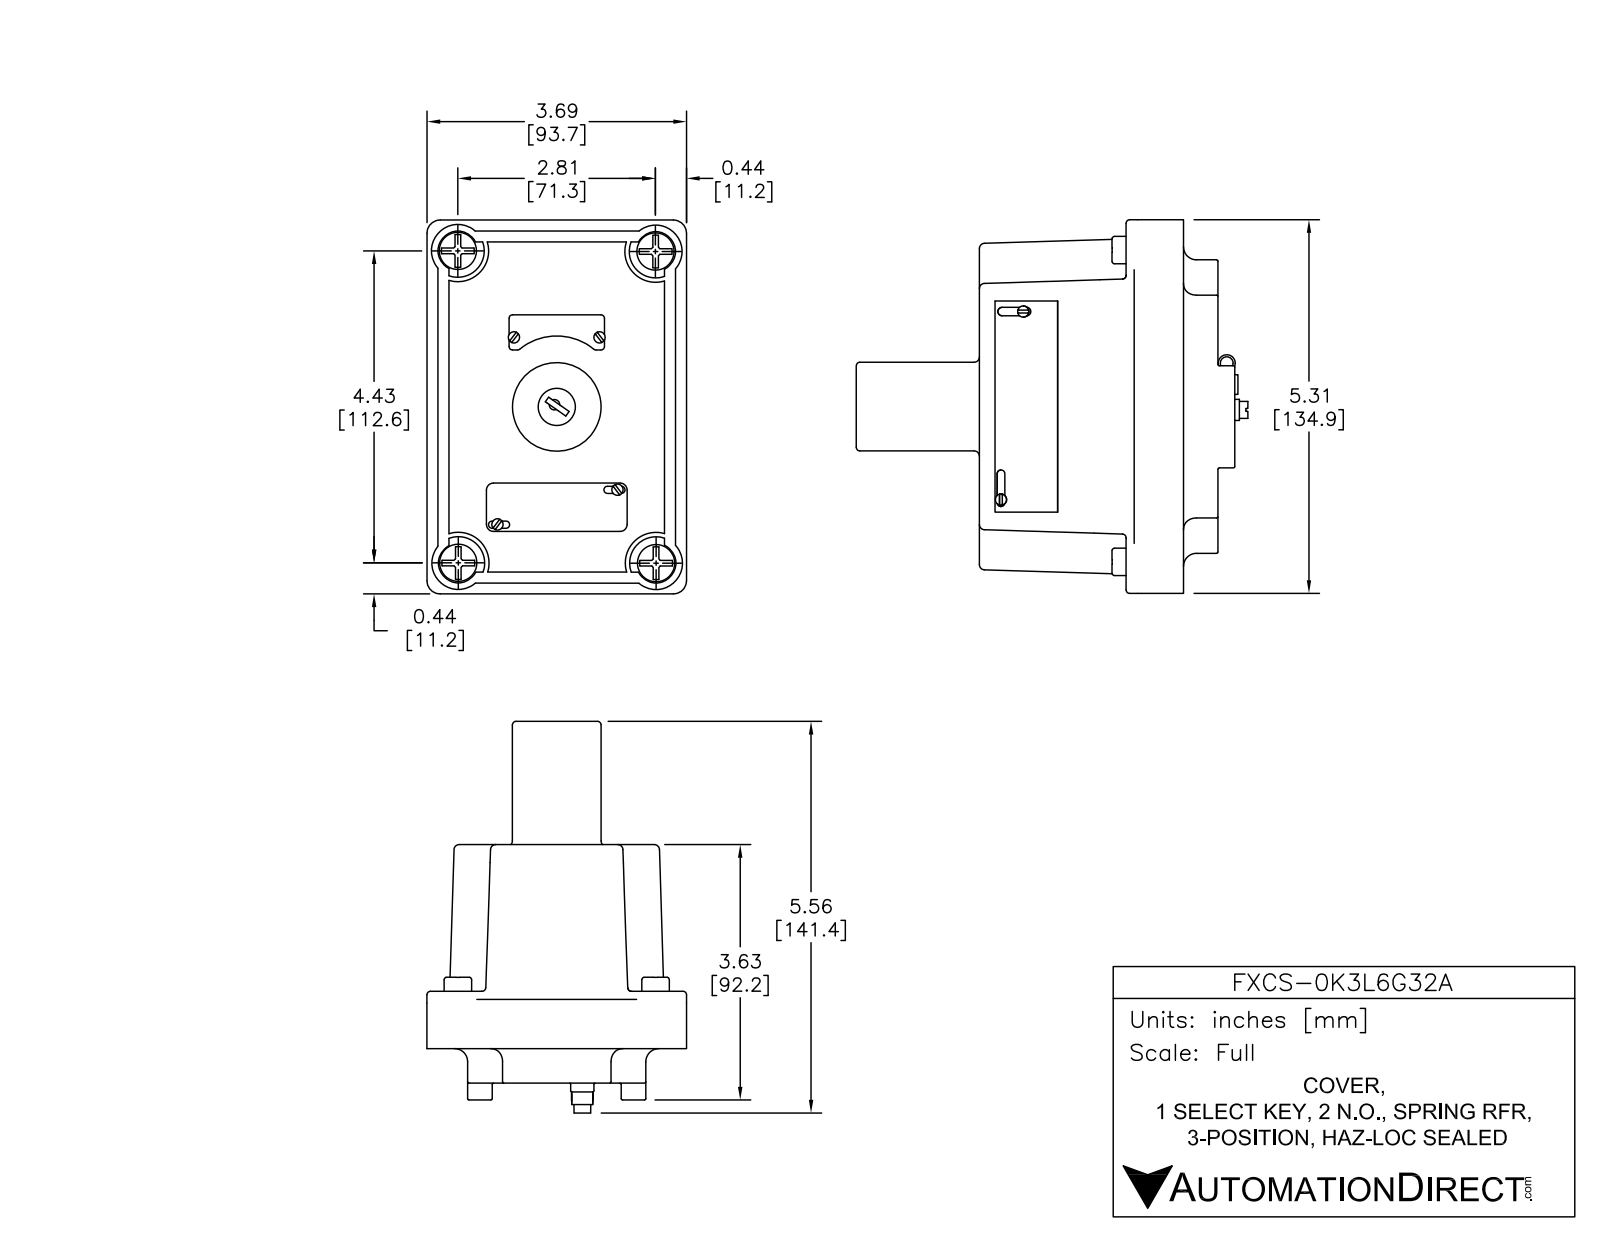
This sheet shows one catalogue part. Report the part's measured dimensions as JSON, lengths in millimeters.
{"part_name": "FXCS-0K3L6G32A", "step_written_by": "SolidWorks 2015 (AUTOMOTIVE_DESIGN)", "units": "millimeters", "bodies": {"solids": 2, "faces": 699, "planar": 303, "cylindrical": 157, "other": 239}, "overall_size": [141.4, 134.9, 93.7], "volume_mm3": 820500, "surface_area_mm2": 63940, "round_holes": [[4.1, 8], [5, 1], [13.4, 1]], "round_bosses_or_shafts": [[4.1, 8], [9.9, 4], [32, 1], [8.4, 1], [7.6, 1], [6.1, 1]], "partial_cylinders_radius": [[1.3, 24], [0.5, 22], [1.3, 4], [1.4, 4], [1.5, 4], [1.9, 4], [2.5, 4], [4.7, 4]], "face_to_face_distances": [86.1, 12.4, 73.7, 0.5, 93.7, 14.7, 79, 30.2, 17.8, 55.9], "hole_center_spacings": [6.4, 55.8, 12.7, 55.4, 56.9, 19.1, 27.7, 28.3]}
